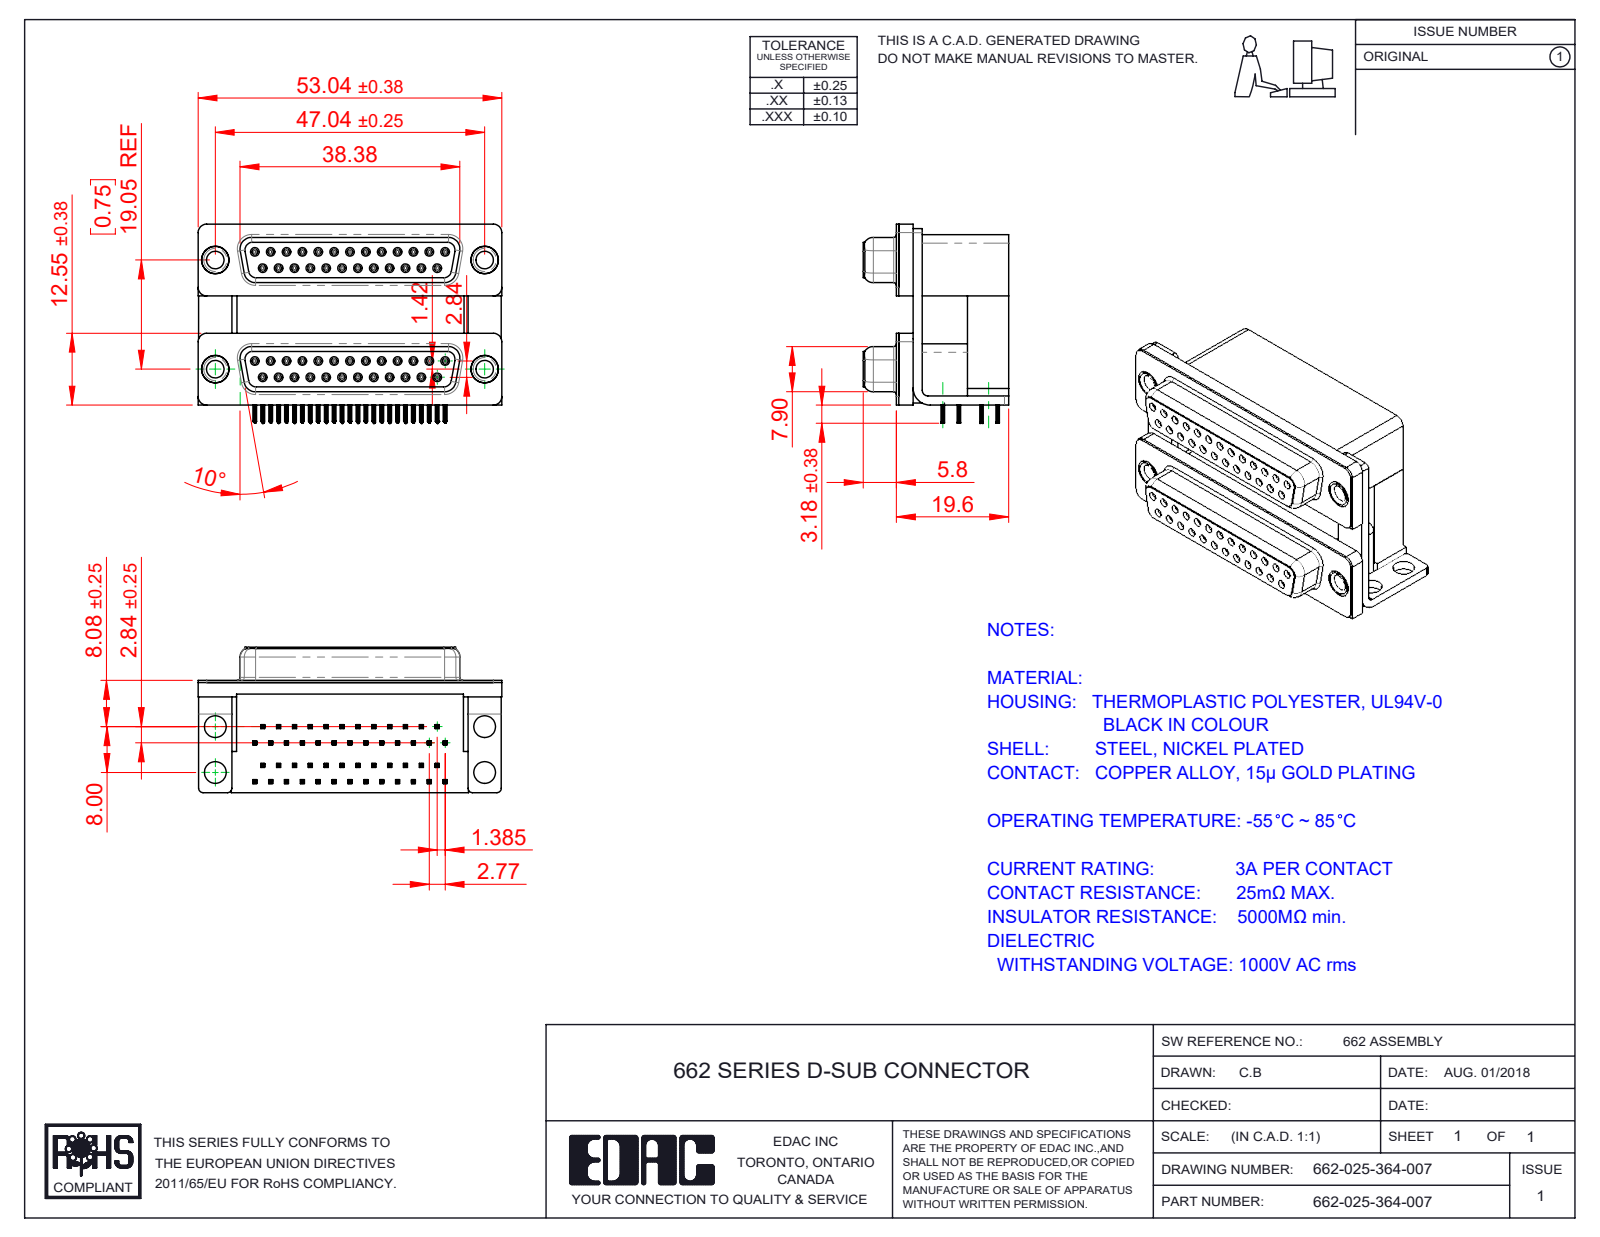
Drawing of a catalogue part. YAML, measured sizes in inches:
part_name: "662 Housing Upper_25 Contacts M; 662 Contact Top Upper_M; 662 Contact Bottom Lower; 662 Thru Hole Rivet (+7 more)"
step_written_by: "SolidWorks 2020 (CONFIG_CONTROL_DESIGN)"
units: inches
bodies: {solids: 61, faces: 7708, planar: 3576, cylindrical: 1768, other: 2364}
overall_size: [2.088, 1.369, 1]
volume: 1.452
surface_area: 39.93
round_holes:
  - {diameter: 0.031, count: 50}
  - {diameter: 0.035, count: 50}
  - {diameter: 0.12, count: 4}
  - {diameter: 0.138, count: 4}
  - {diameter: 0.15, count: 4}
  - {diameter: 0.157, count: 4}
  - {diameter: 0.189, count: 4}
  - {diameter: 0.197, count: 4}
round_bosses_or_shafts:
  - {diameter: 0.047, count: 50}
  - {diameter: 0.193, count: 4}
  - {diameter: 0.187, count: 4}
  - {diameter: 0.152, count: 4}
partial_cylinders:
  - {radius: 0.004, count: 400}
  - {radius: 0.006, count: 200}
  - {radius: 0.014, count: 100}
  - {radius: 0.013, count: 50}
  - {radius: 0.011, count: 24}
  - {radius: 0.053, count: 16}
  - {radius: 0.059, count: 14}
  - {radius: 0.02, count: 8}
face_to_face_distances: [0.756, 0.75, 0.472, 0.016, 0.283, 0.244, 0.421, 0.098, 0.488, 0.657]
hole_center_spacings: [0.124, 0.109, 0.218, 0.436, 0.327, 0.198, 0.545, 0.294]
